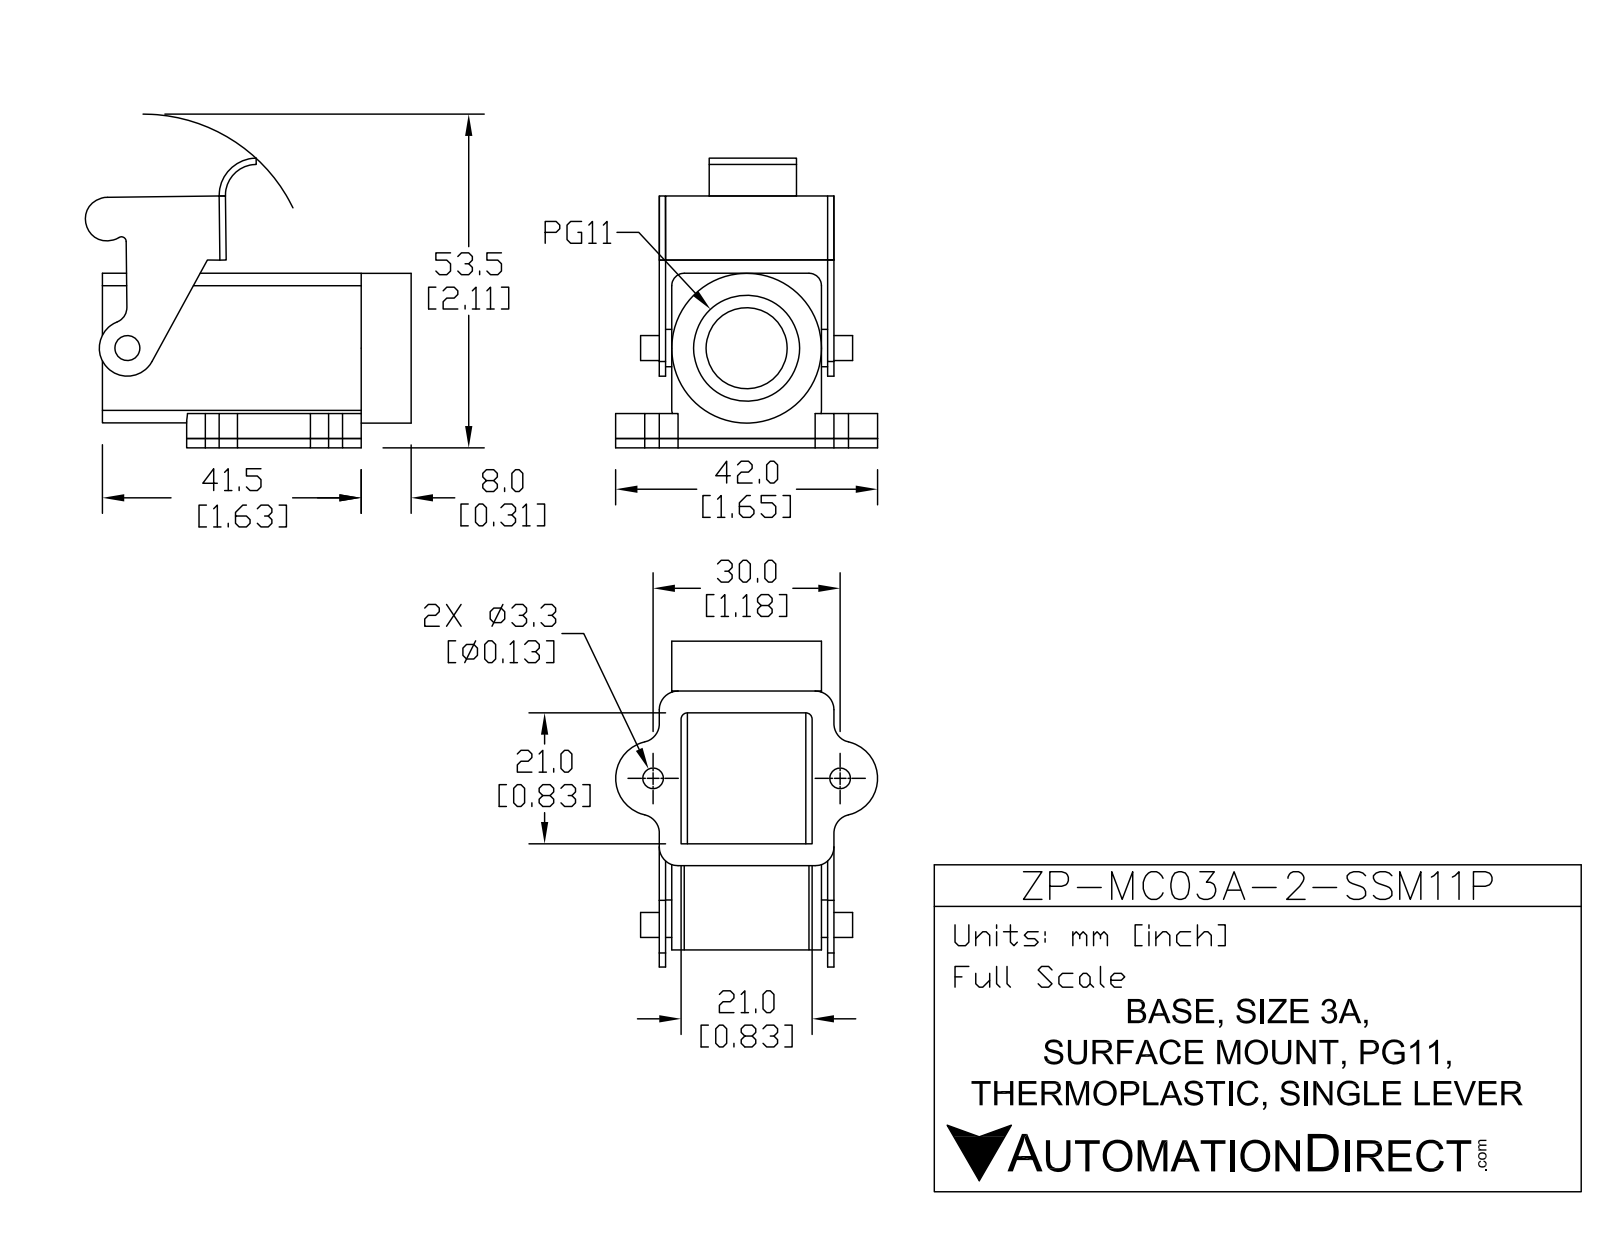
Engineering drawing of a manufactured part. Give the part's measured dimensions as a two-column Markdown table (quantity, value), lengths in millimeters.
| quantity | value |
| --- | --- |
| part name | ZP-MC03A-2-SSM11P |
| STEP written by | SolidWorks 2011 (AUTOMOTIVE_DESIGN) |
| units | millimeters |
| bodies | 2 solids, 126 faces (58 planar, 65 cylindrical, 3 other) |
| overall size | 56.44 × 54.59 × 42 |
| volume | 12 803 mm³ |
| surface area | 13 678 mm² |
| round holes (diameter × count) | 3.3 × 2, 3 × 1, 13 × 1, 17 × 1 |
| round bosses / shafts (diameter × count) | 24 × 1, 6 × 1, 4 × 1 |
| partial cylindrical surfaces (radius × count) | 2 × 10, 3 × 8, 1 × 6, 6 × 2, 0.5 × 1, 1 × 1, 3.45 × 1, 3.73 × 1 |
| main face-to-face distances | 1.5, 22.5, 21, 25, 26.5, 24, 2.5, 2.56, 4, 1 |
| hole center spacings | 22.3, 30 |
